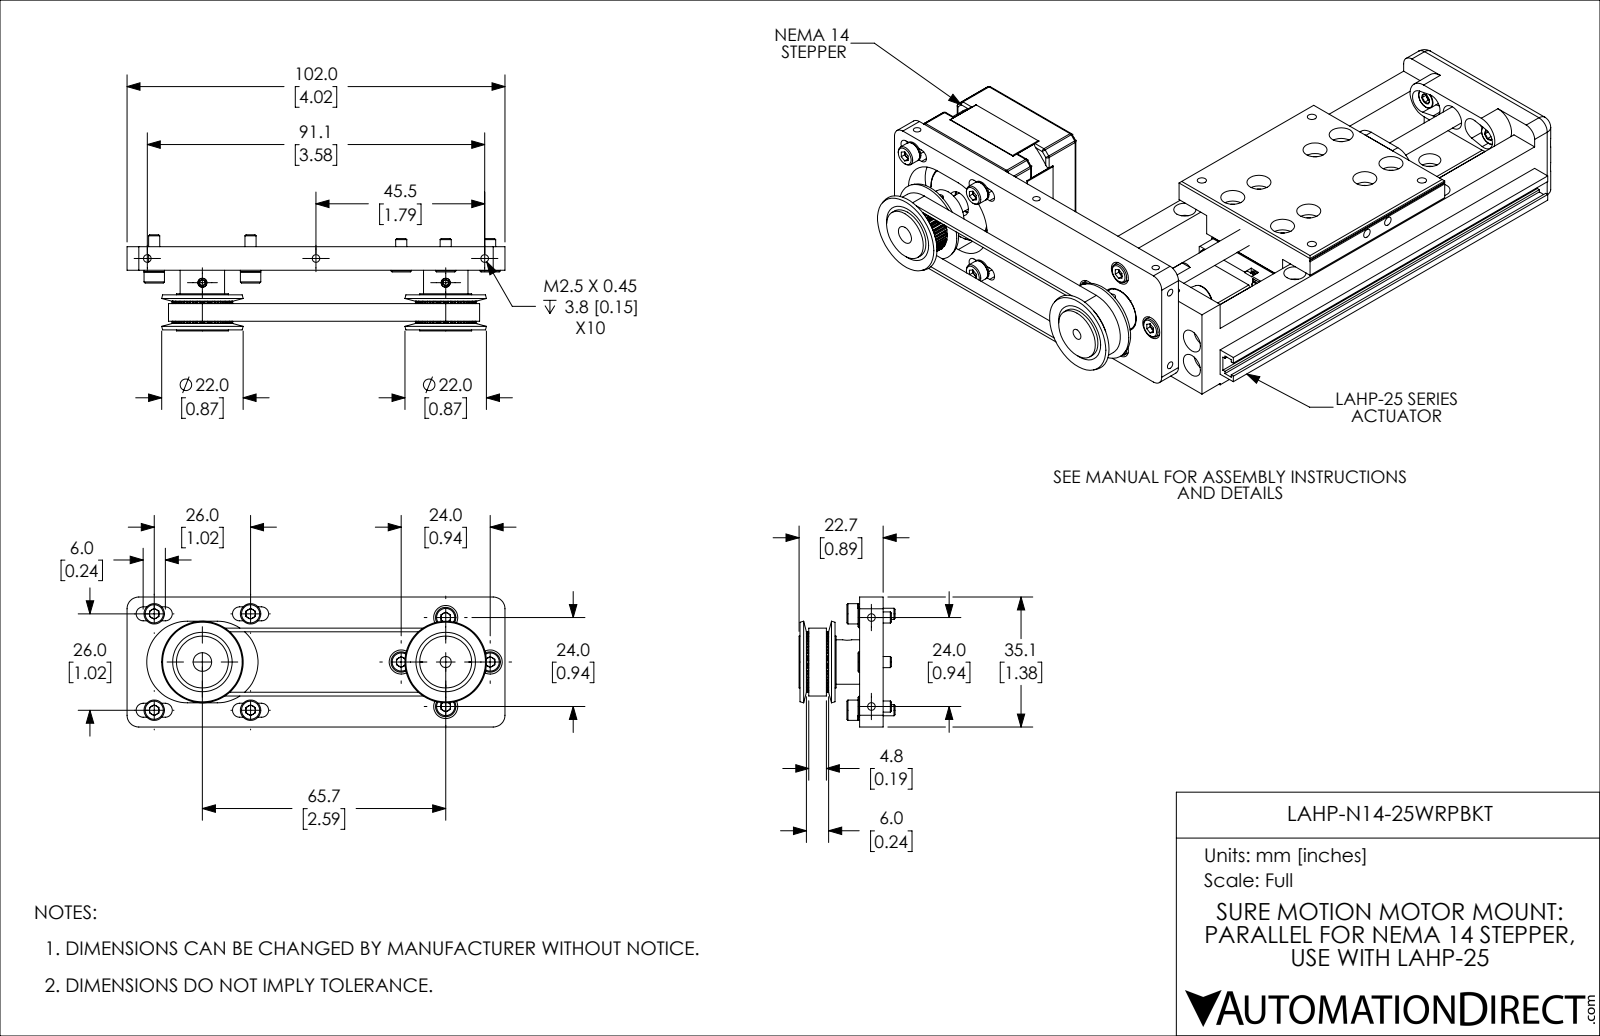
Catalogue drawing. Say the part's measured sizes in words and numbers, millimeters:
The part is named "LAHP-N14-25WRPBKT". Its 3-D file was written by "SolidWorks 2019 (CONFIG_CONTROL_DESIGN)". It is 24 solids with 1079 faces: 436 planar, 516 cylindrical and 127 other. Overall it measures 102 by 35.1 by 25.9 millimeters. Its volume is 24 200 cubic millimeters and its surface area 17 690 square millimeters. Round holes: 8 of diameter 3.2, 7 of diameter 2.1, 4 of diameter 3.4, 4 of diameter 6.5, 3 of diameter 2.5, 1 of diameter 2.5, 1 of diameter 3, 1 of diameter 5, 1 of diameter 12.5. Round bosses or shafts: 12 of diameter 3, 8 of diameter 5.5, 2 of diameter 14, 2 of diameter 12. Partial cylindrical surfaces (rounded edges, fillets, slot ends): 104 of radius 0.2, 104 of radius 0.3, 8 of radius 1.9, 4 of radius 3.2, 2 of radius 7.5, 2 of radius 8.2, 2 of radius 9.1, 2 of radius 11. The main face-to-face distances are 6.4, 1, 17.3, 35.1, 9.4, 3, 8.4, 9.4, 26.7, 25.7. The hole center spacings are 45.5, 12, 17, 18.4, 26, 24, 31.3, 36.8.
